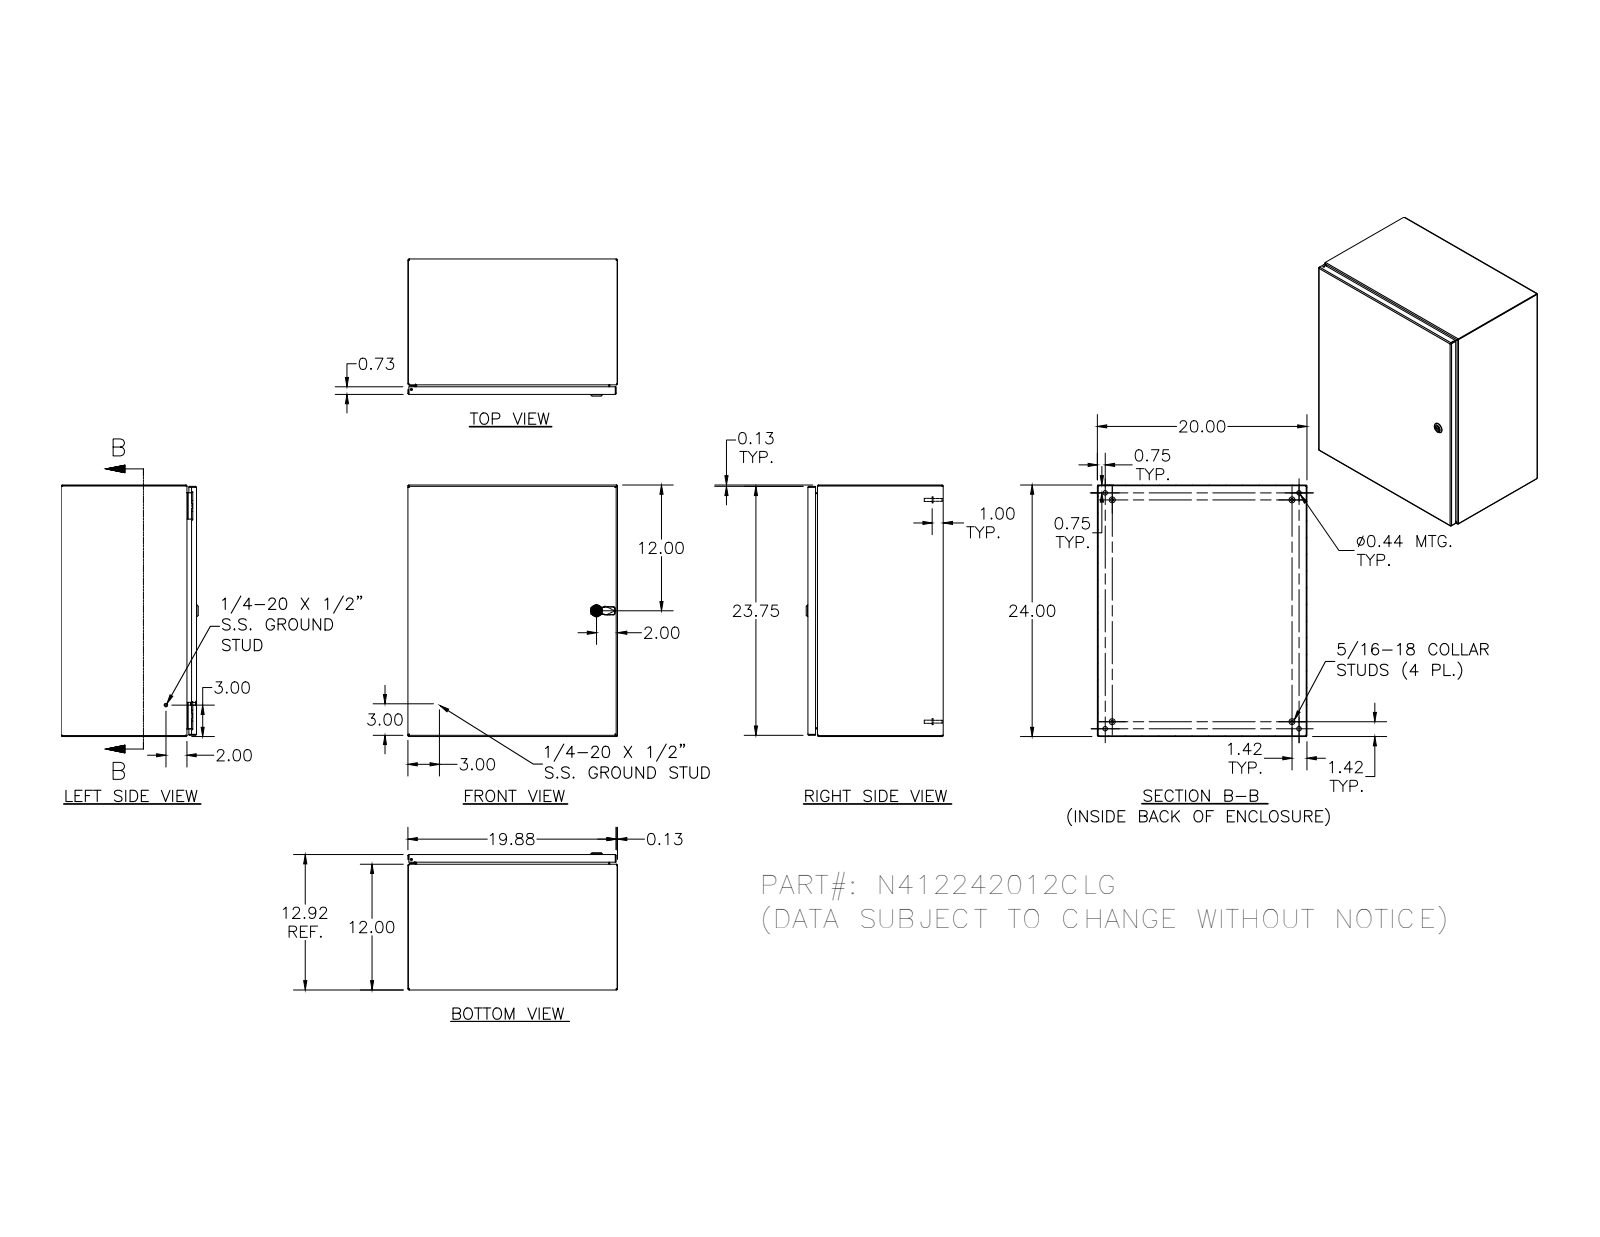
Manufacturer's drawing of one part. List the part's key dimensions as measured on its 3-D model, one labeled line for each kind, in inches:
Part name (STEP PRODUCT): N412242012CLG
STEP written by: SolidWorks 2018 (AUTOMOTIVE_DESIGN)
Units: inches
Bodies: 33 solids, 1449 faces (530 planar, 547 cylindrical, 372 other)
Overall size (bounding box): 24 × 20 × 13.075
Volume: 162.1 in³ · Surface area: 4 404 in²
Round holes (diameter × count): ⌀0.188 ×5, ⌀0.093 ×4, ⌀0.152 ×4, ⌀0.167 ×4, ⌀0.172 ×4, ⌀0.437 ×4, ⌀0.156 ×2, ⌀0.187 ×1, ⌀0.197 ×1, ⌀0.315 ×1, ⌀0.394 ×1, ⌀0.402 ×1
Round bosses / shafts (diameter × count): ⌀0.25 ×10, ⌀0.563 ×4, ⌀0.36 ×4, ⌀0.32 ×4, ⌀0.3 ×4, ⌀0.256 ×4, ⌀0.164 ×4, ⌀0.131 ×4
Partial cylindrical surfaces — rounded edges, fillets, slot ends (radius × count): R0.012 ×30, R0.031 ×30, R0.05 ×26, R0.105 ×20, R0.016 ×18, R0.125 ×16, R0.02 ×13, R0.032 ×8
Main face-to-face distances: 0.074, 12.843, 0.074, 12.769, 12.917, 19.926, 20, 19.852, 19.926, 23.926
Hole centre spacings: 20, 0.66, 0.656, 1.307, 1.965, 18.872, 0.5, 0.984
